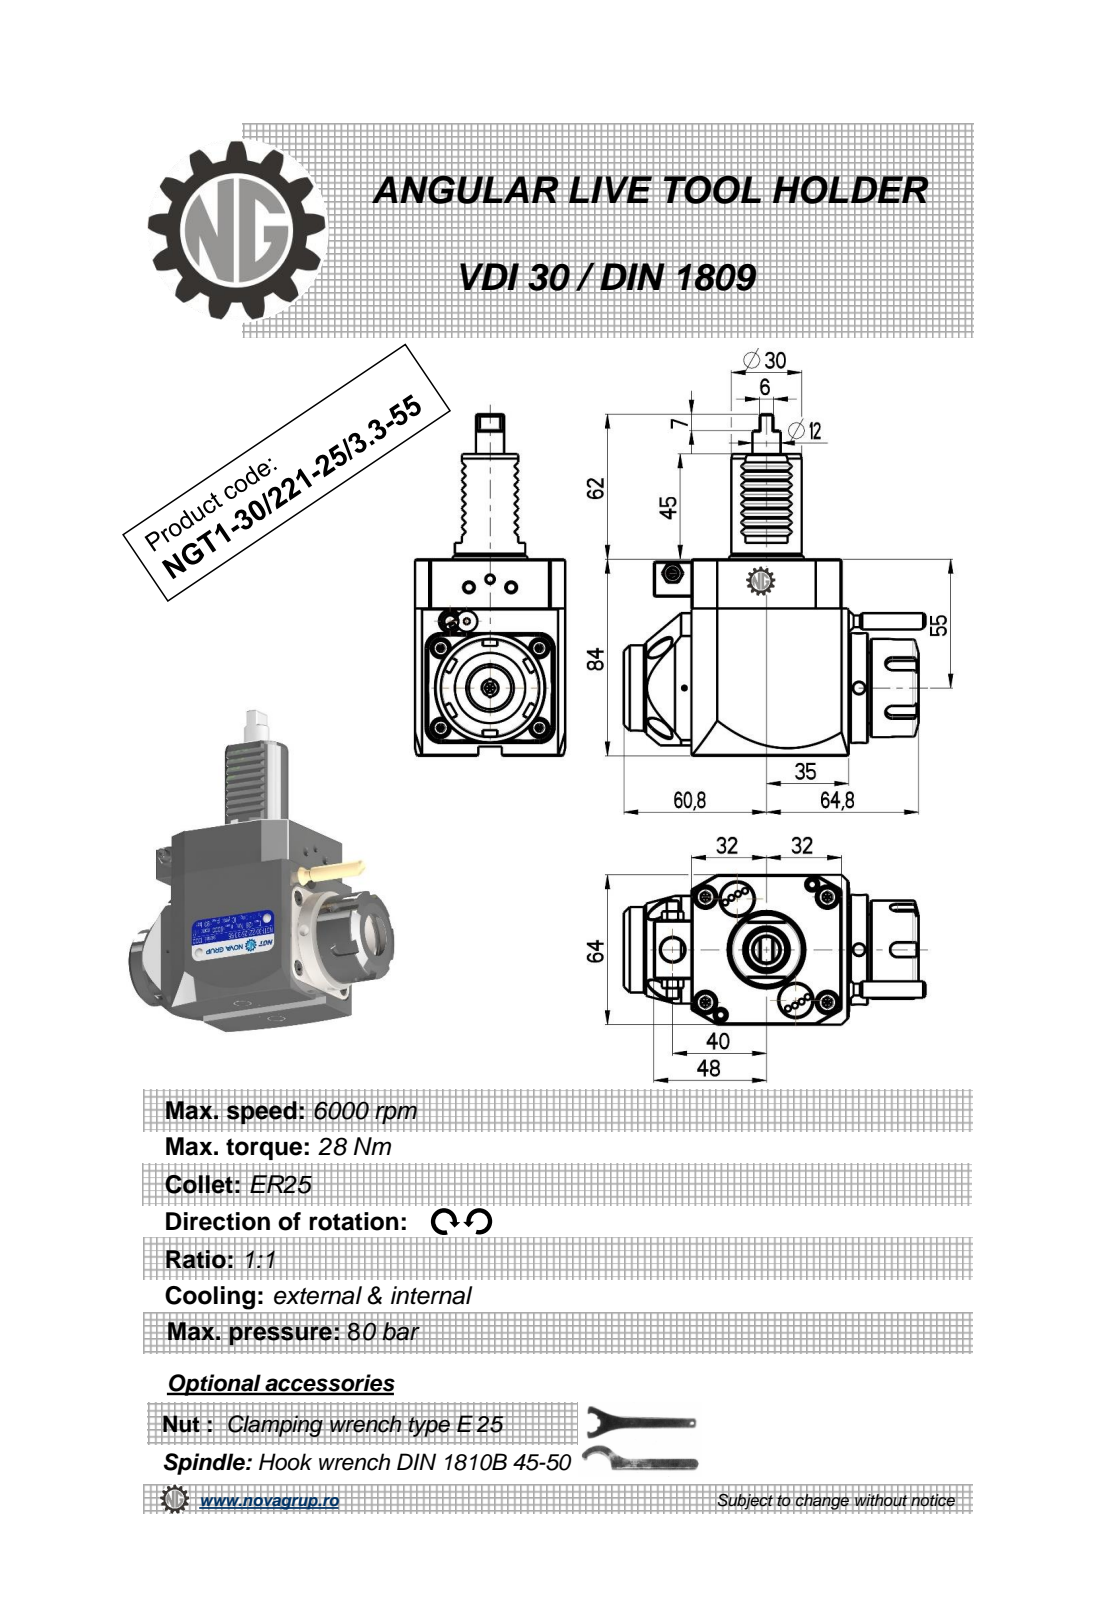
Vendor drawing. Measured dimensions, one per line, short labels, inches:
name: NGT1_30_221_25_3_3_55
written by: PRO/ENGINEER BY PARAMETRIC TECHNOLOGY CORPORATION, 2010280 (CONFIG_CONTROL_DESIGN)
unit: in
bodies: 1 solid, 457 faces (215 planar, 90 cylindrical, 152 other)
size: 5.748 × 5.064 × 2.52
volume: 28.56 in³; area: 74.2 in²
holes: 2× ⌀0.197, 1× ⌀0.098, 1× ⌀0.118, 1× ⌀0.165, 1× ⌀0.374, 1× ⌀0.394, 1× ⌀0.799
bosses: 2× ⌀0.353, 2× ⌀0.197, 1× ⌀1.85, 1× ⌀1.654, 1× ⌀1.437, 1× ⌀1.378, 1× ⌀1.181, 1× ⌀0.472
rounds: 16× R0.012, 12× R0.01, 5× R0.118, 2× R0.031, 2× R6.299, 1× R1.26
face distances: 2.52, 3.307, 0.02, 2.646, 2.638, 0.118, 0.126, 0.295, 0.111, 3.15
hole spacings: 0.975, 1.307, 1.831, 3.128, 3.675
